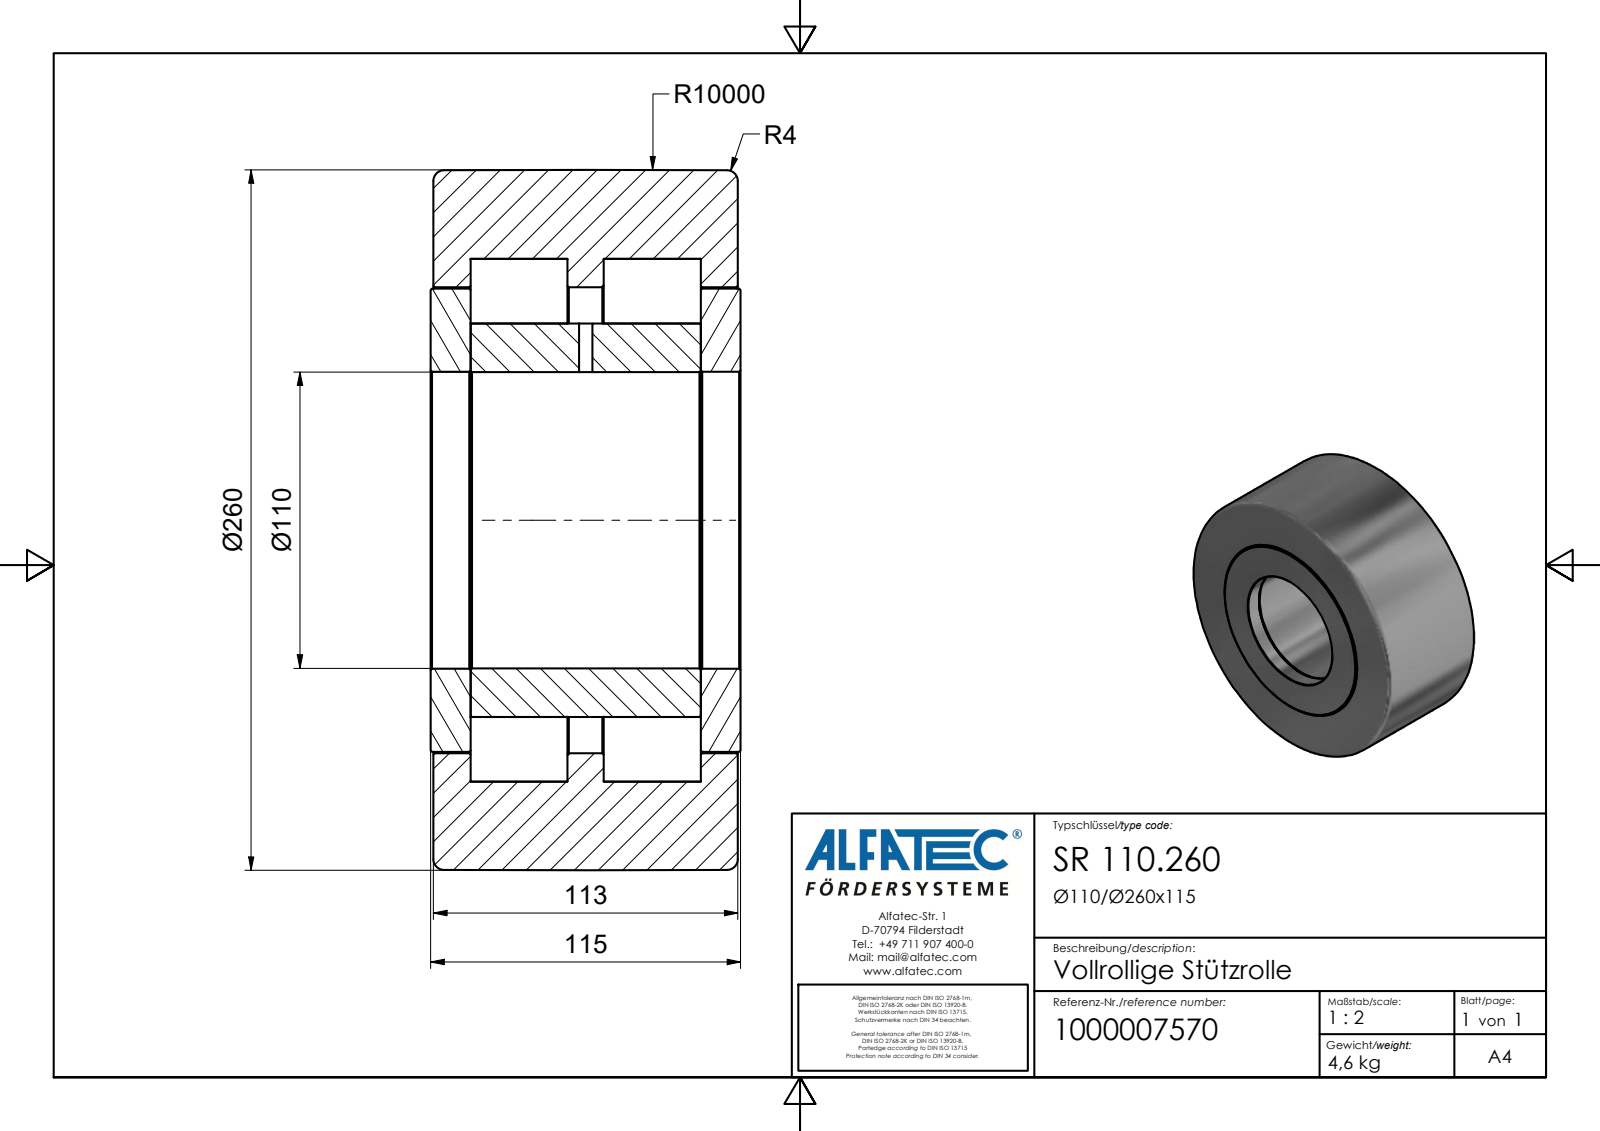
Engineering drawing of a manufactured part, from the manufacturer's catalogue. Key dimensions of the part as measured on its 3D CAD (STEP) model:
Part name (STEP PRODUCT): SR 110.260_Kontur
STEP written by: Autodesk Inventor 2020 (AUTOMOTIVE_DESIGN)
Units: millimetres
Bodies: 1 solid, 312 faces (100 planar, 103 cylindrical, 109 other)
Overall size (bounding box): 260 × 260 × 115
Volume: 4 636 000 mm³ · Surface area: 480 860 mm²
Round holes (diameter × count): ⌀5 ×1, ⌀110 ×1, ⌀110.2 ×1, ⌀173 ×1, ⌀194 ×1
Round bosses / shafts (diameter × count): ⌀24 ×22, ⌀172 ×1, ⌀146 ×1
Main face-to-face distances: 1, 114, 113, 50.75, 64.25, 49.75, 63.25, 115, 14.75, 100.25
